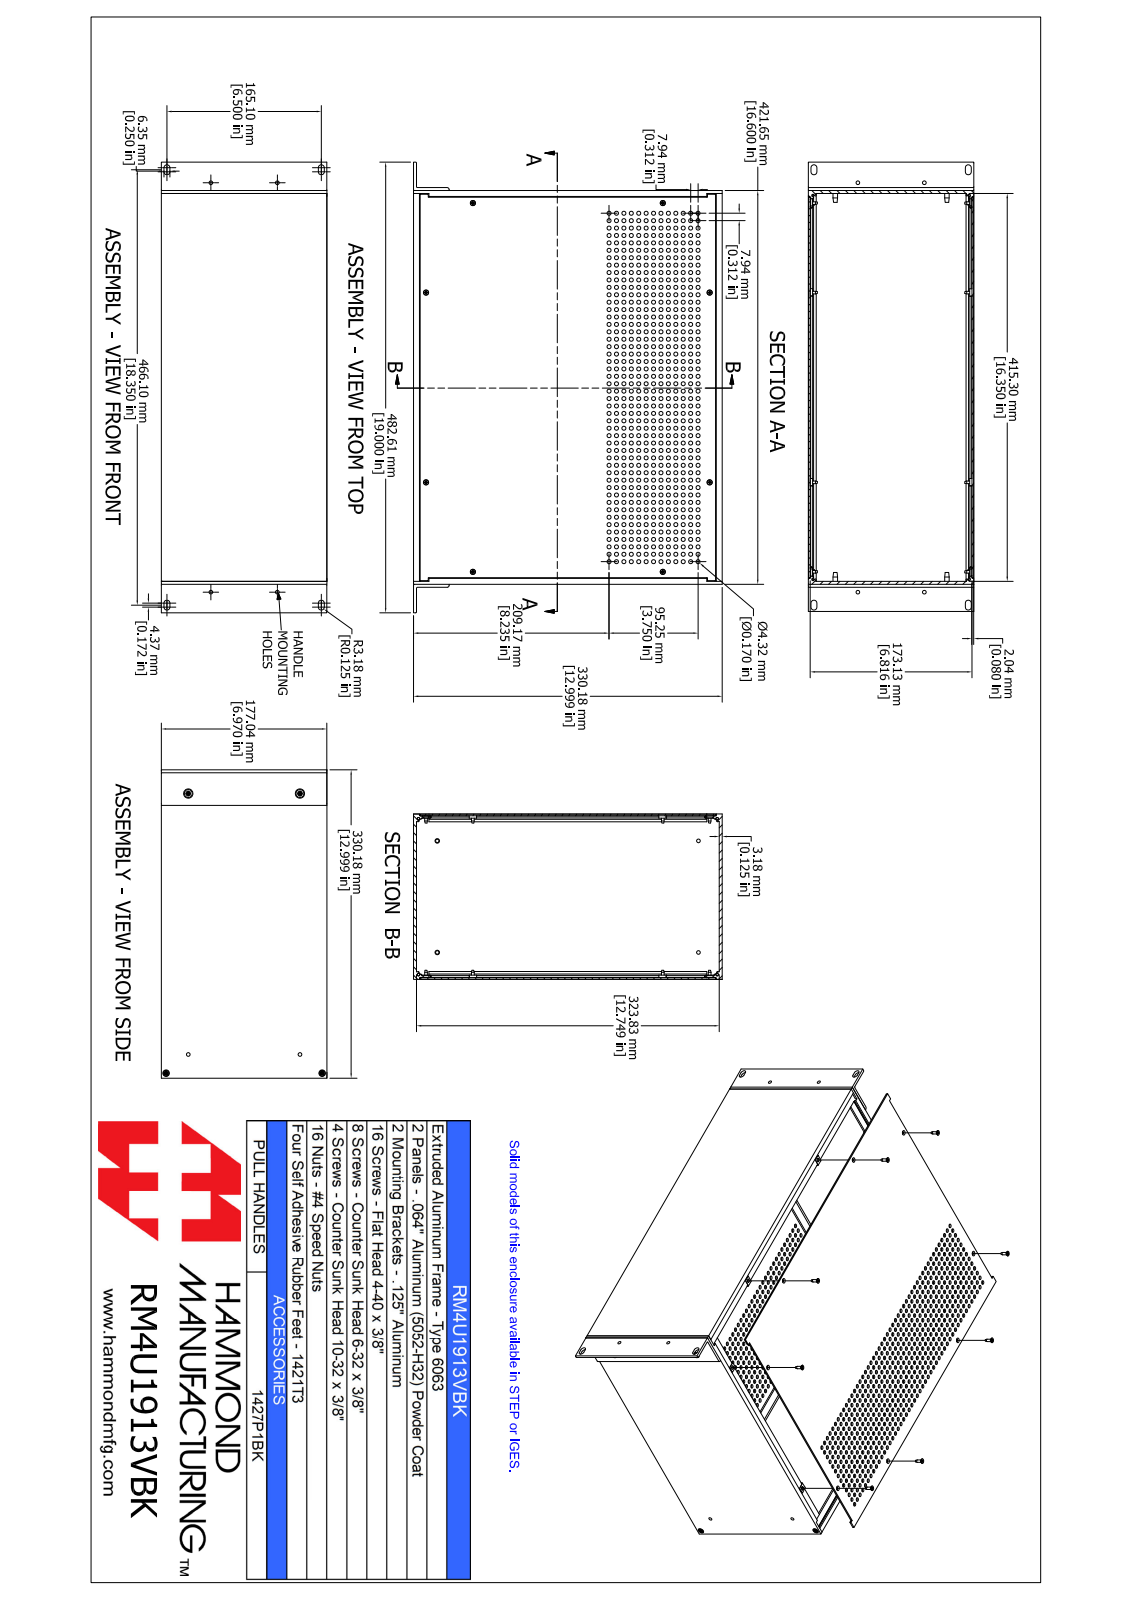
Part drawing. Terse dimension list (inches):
name: RM4U1913VBK
written by: SolidWorks 2021 (AUTOMOTIVE_DESIGN)
unit: in
bodies: 52 solids, 2620 faces (636 planar, 1488 cylindrical, 496 other)
size: 19 × 12.999 × 6.971
volume: 89.41 in³; area: 1 869 in²
holes: 624× ⌀0.17, 10× ⌀0.118, 8× ⌀0.098, 8× ⌀0.157, 4× ⌀0.138, 4× ⌀0.156, 4× ⌀0.157, 4× ⌀0.165, 4× ⌀0.169, 2× ⌀0.197
bosses: 9× ⌀0.214, 9× ⌀0.112, 4× ⌀0.238, 4× ⌀0.138, 2× ⌀0.333, 2× ⌀0.19
rounds: 22× R0.039, 16× R0.015, 16× R0.038, 16× R0.049, 8× R0.055, 8× R0.125, 8× R0.131, 2× R0.079
face distances: 0.071, 6.887, 0.125, 6.816, 6.958, 16.475, 0.125, 12.874, 12.999, 12.749
hole spacings: 1.25, 0.313, 0.937, 1.563, 2.5, 8, 0.625, 0.625
